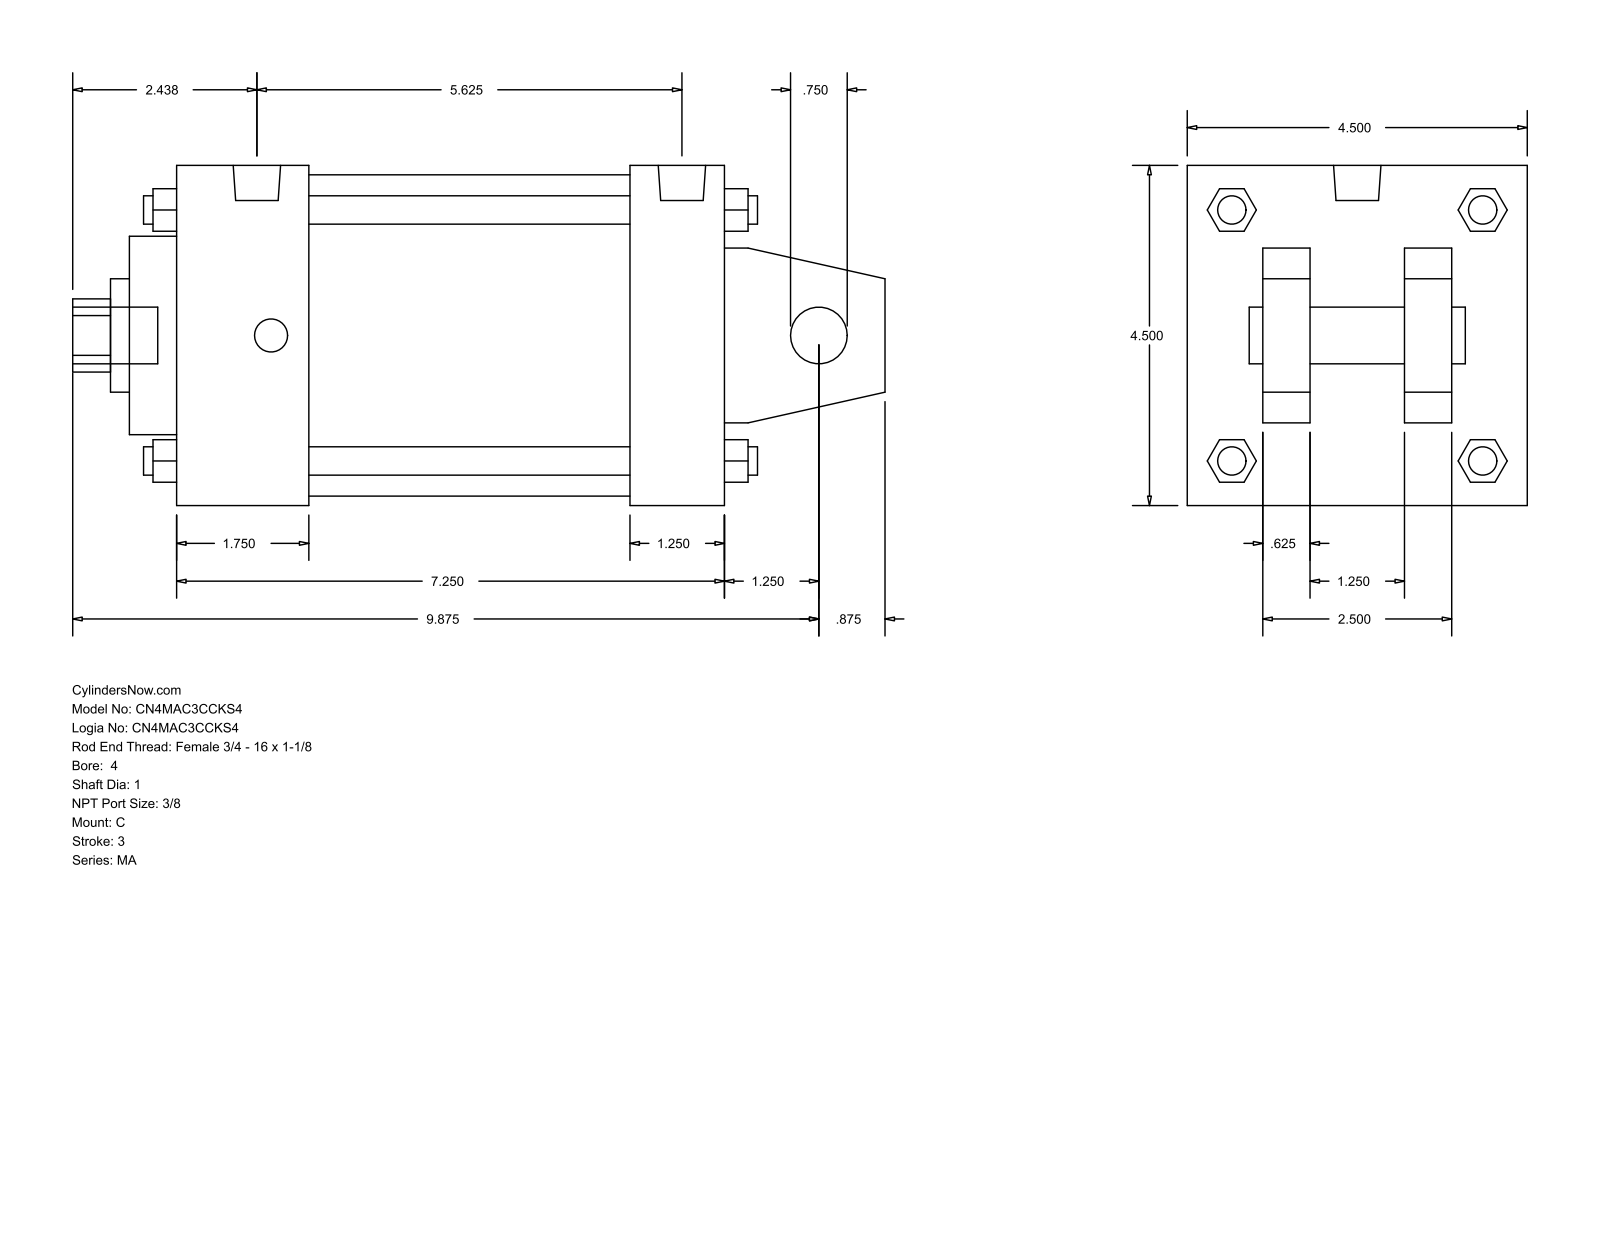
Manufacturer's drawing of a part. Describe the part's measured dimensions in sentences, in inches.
The part is named "MA_C__0400_1". Its 3-D file was written by "GSSL Pune (CONFIG_CONTROL_DESIGN)". It is 0 solids with 141 faces: 109 planar, 32 cylindrical and 0 other. Overall it measures 10.75 by 4.5 by 4.5 inches. Round holes: 1 of diameter 0.75, 1 of diameter 1, 1 of diameter 1.5, 1 of diameter 2.625, 1 of diameter 4.25. Round bosses or shafts: 4 of diameter 0.437, 4 of diameter 0.375, 2 of diameter 0.627, 1 of diameter 0.75. Partial cylindrical surfaces (rounded edges, fillets, slot ends): 1 of radius 0.484. The main face-to-face distances are 4.5, 7.25, 0.625, 2.875, 1.625, 1, 3.5, 1.875, 6, 1.25.
